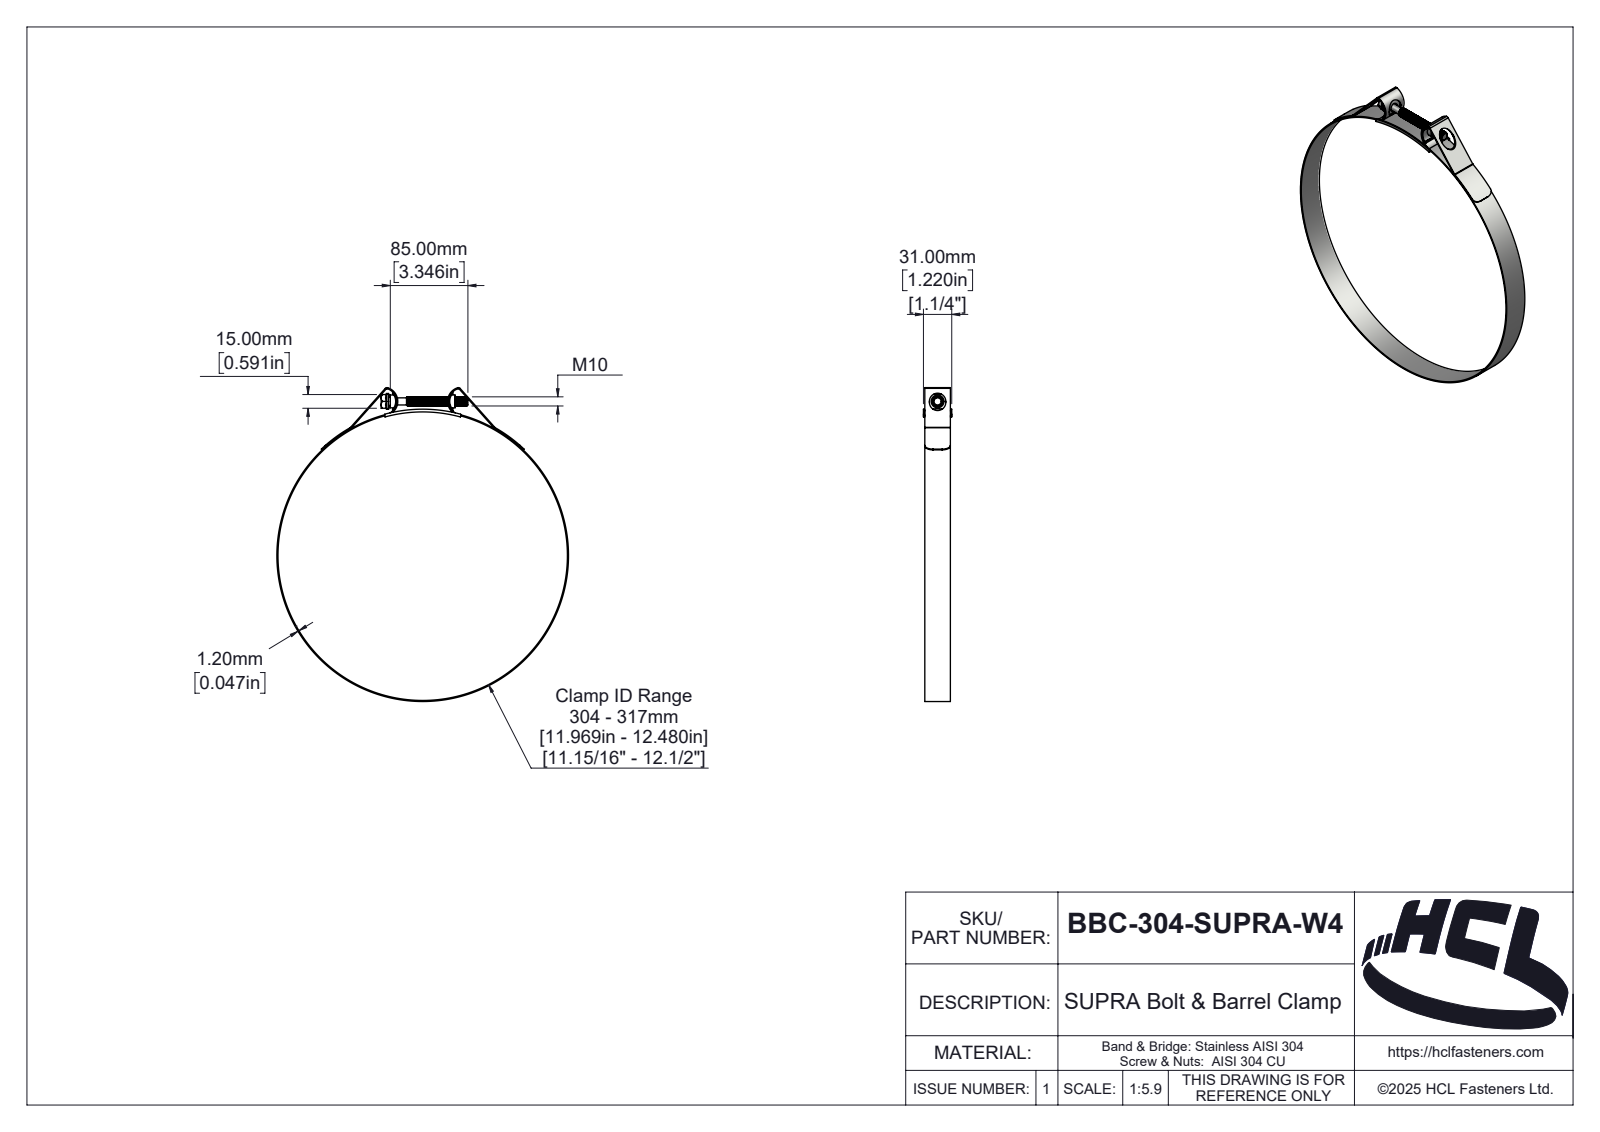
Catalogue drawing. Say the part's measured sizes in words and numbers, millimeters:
The part is named "BBC-304-SUPRA-W4". Its 3-D file was written by "SolidWorks 2025 (AUTOMOTIVE_DESIGN)". It is 5 solids with 379 faces: 50 planar, 243 cylindrical and 86 other. Overall it measures 343.61 by 319.4 by 31 millimeters. Its volume is 51 458 cubic millimeters and its surface area 81 404 square millimeters. Round holes: 1 of diameter 317. Round bosses or shafts: 1 of diameter 319.4, 1 of diameter 17.32, 1 of diameter 14, 1 of diameter 10, 1 of diameter 7.8. Partial cylindrical surfaces (rounded edges, fillets, slot ends): 4 of radius 1, 2 of radius 1.3, 2 of radius 2, 2 of radius 2.5, 2 of radius 3.2, 2 of radius 9, 2 of radius 13.39, 2 of radius 14.39. The main face-to-face distances are 1.2, 28, 1.5, 29.5, 29.8, 28.3, 31, 28.6, 15, 2.5.
